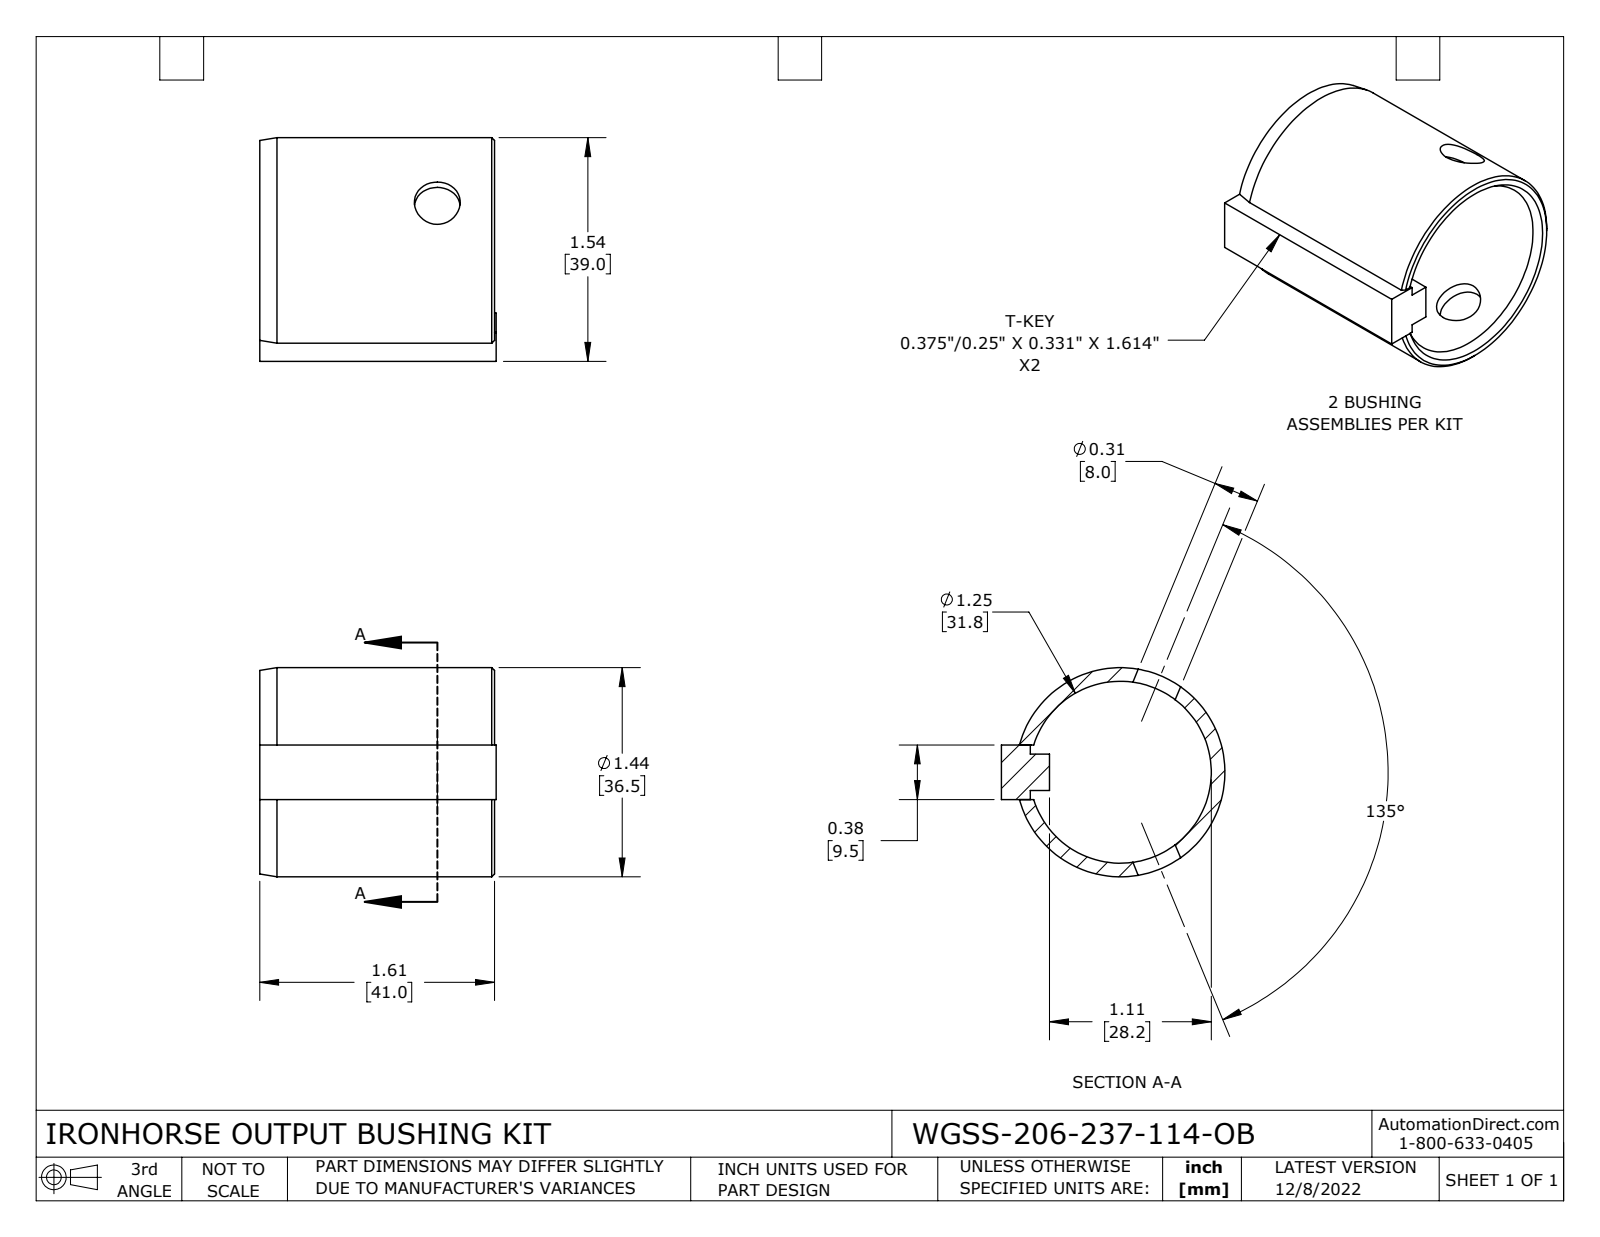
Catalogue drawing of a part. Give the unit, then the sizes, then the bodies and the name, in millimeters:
Units: millimetres
Overall size (bounding box): 41.28 × 39.04 × 36.51
Round holes (diameter × count): ⌀8 ×2, ⌀31.75 ×1
Round bosses / shafts (diameter × count): ⌀36.51 ×1
Main face-to-face distances: 9.53, 1.59, 7.94, 8.42, 6.35, 3.38, 5.04, 41, 41.28, 1.58
Volume: 11 943 mm³ · Surface area: 10 011 mm²
Bodies: 2 solids, 34 faces (16 planar, 6 cylindrical, 12 other)
Part name (STEP PRODUCT): WGSS-206-237-114-OB
STEP written by: SolidWorks 2021 (CONFIG_CONTROL_DESIGN)
